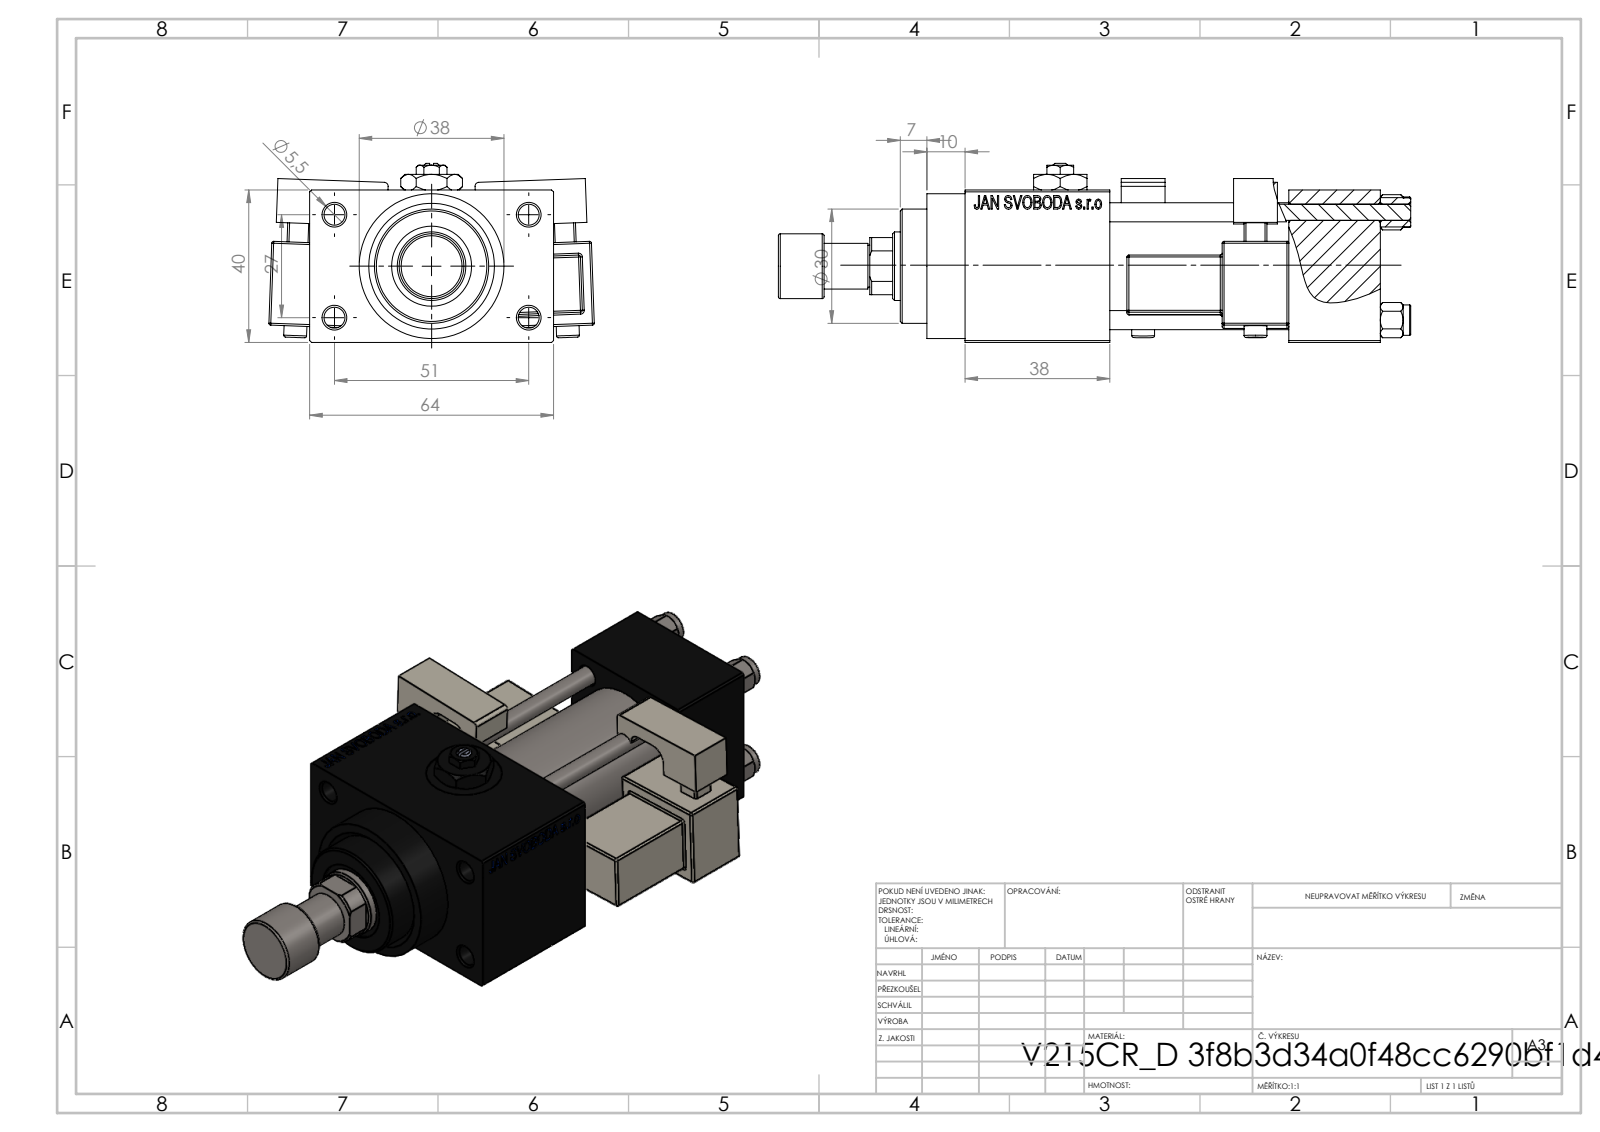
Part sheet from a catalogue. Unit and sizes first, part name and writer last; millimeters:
Units: millimetres
Overall size (bounding box): 166 × 85.39 × 47
Round holes (diameter × count): ⌀5 ×4, ⌀5.5 ×4, ⌀20 ×4, ⌀13.16 ×3, ⌀7 ×2, ⌀8.5 ×1, ⌀18 ×1, ⌀21 ×1, ⌀25 ×1, ⌀30 ×1
Round bosses / shafts (diameter × count): ⌀8 ×4, ⌀6 ×2, ⌀38 ×1, ⌀31 ×1, ⌀17 ×1, ⌀12 ×1, ⌀11 ×1
Partial cylindrical surfaces — rounded edges, fillets, slot ends (radius × count): R0.5 ×48, R1 ×2, R2.5 ×2, R4 ×2
Main face-to-face distances: 40, 47, 12, 24, 38, 3, 20, 71, 52, 109
Hole centre spacings: 11.37, 20.01, 28.3, 28.85, 29.89, 39.66, 48.34, 27
Volume: 223 809 mm³ · Surface area: 78 673 mm²
Bodies: 15 solids, 1320 faces (584 planar, 156 cylindrical, 580 other)
Part name (STEP PRODUCT): V215CR_D_Body; V215_VC_A; V215CR_D_TYCINKA; NUT_M5_D (+4 more)
STEP written by: SolidWorks 2019 (CONFIG_CONTROL_DESIGN)
